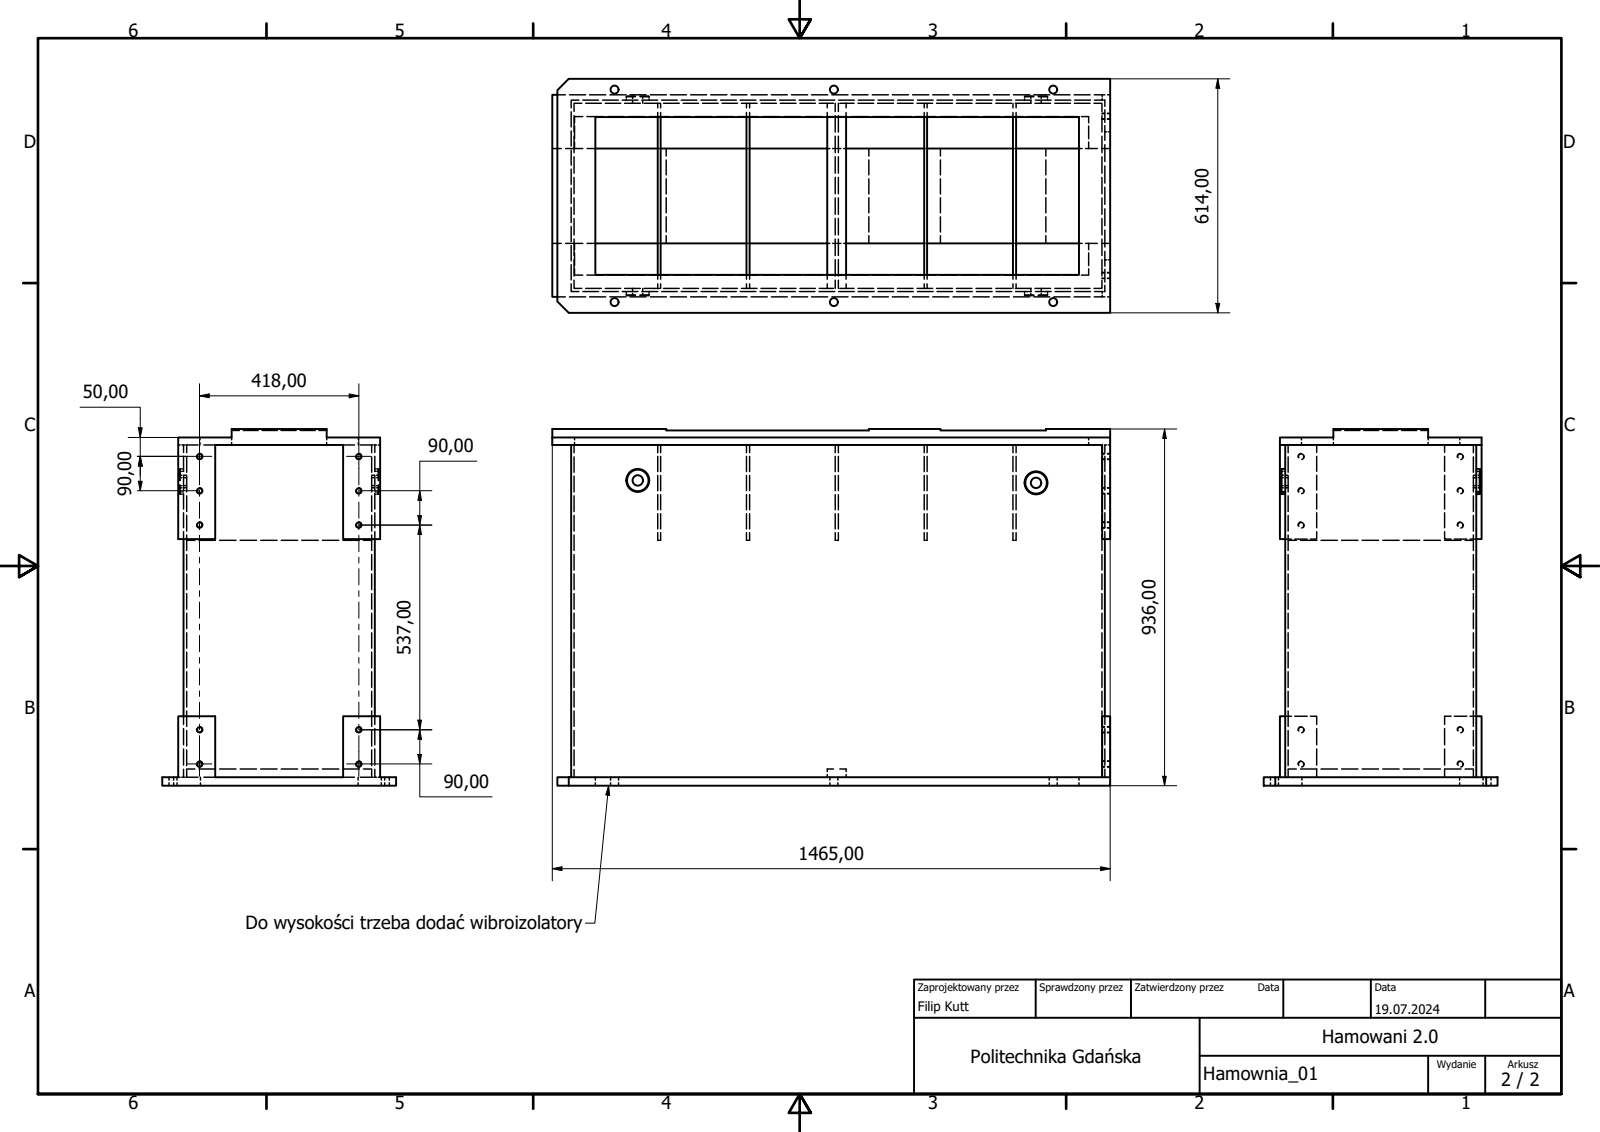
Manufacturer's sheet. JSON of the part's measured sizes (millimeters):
{"part_name": "Hamownia_01; Fundament_01; Profil_R_01; Profil_L_01 (+8 more)", "step_written_by": "Autodesk Inventor 2024 (AUTOMOTIVE_DESIGN)", "units": "millimeters", "bodies": {"solids": 12, "faces": 580, "planar": 406, "cylindrical": 166, "other": 8}, "overall_size": [2293, 1210.23, 620.76], "volume_mm3": 159000000, "surface_area_mm2": 16150000, "round_holes": [[13.84, 30], [10, 8], [21, 6], [27, 2], [38, 1]], "round_bosses_or_shafts": [[60, 5], [54, 5], [50, 4], [180, 1], [160, 1], [40, 1], [26, 1]], "partial_cylinders_radius": [[9, 92], [6, 2]], "face_to_face_distances": [8, 494.14, 502.14, 486.14, 233.33, 22, 1394, 22.01, 700, 454.13], "hole_center_spacings": [110, 220, 517.81, 551.75, 330, 474.91, 506, 604.1]}
